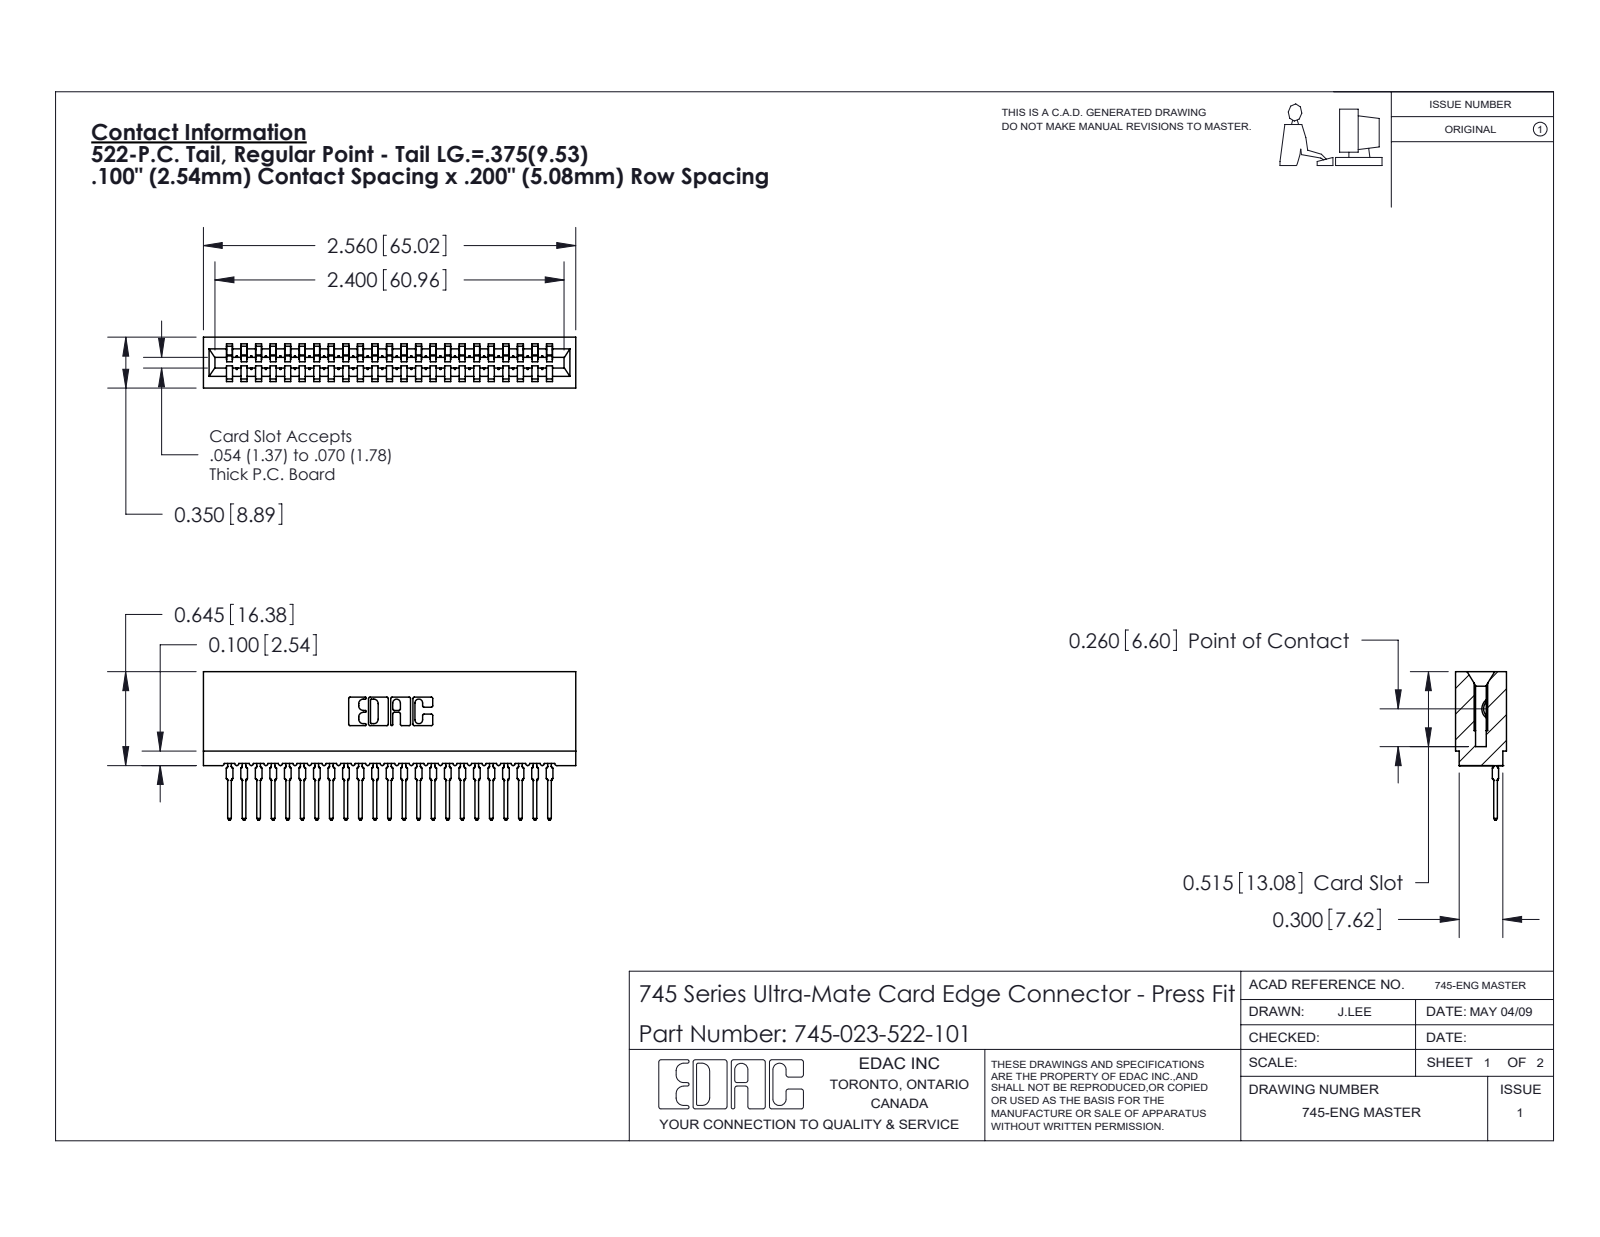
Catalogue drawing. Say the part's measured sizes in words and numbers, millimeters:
The part is named "745 Part_Insulator Option - 01; 745-292-001_522; 745-023-522-101". Its 3-D file was written by "SolidWorks 2020 (CONFIG_CONTROL_DESIGN)". It is 24 solids with 2671 faces: 1596 planar, 477 cylindrical and 598 other. Overall it measures 65 by 25.9 by 8.9 millimeters. Its volume is 5 770 cubic millimeters and its surface area 10 440 square millimeters. Partial cylindrical surfaces (rounded edges, fillets, slot ends): 46 of radius 0.4, 46 of radius 0.5, 22 of radius 0.3, 6 of radius 0.2, 6 of radius 0.8, 4 of radius 0.1, 4 of radius 0.3, 3 of radius 0.7. The main face-to-face distances are 5.1, 2.5, 7.6, 8.9, 10.2, 12.7, 15.2, 3.5, 5.4, 1.1.
